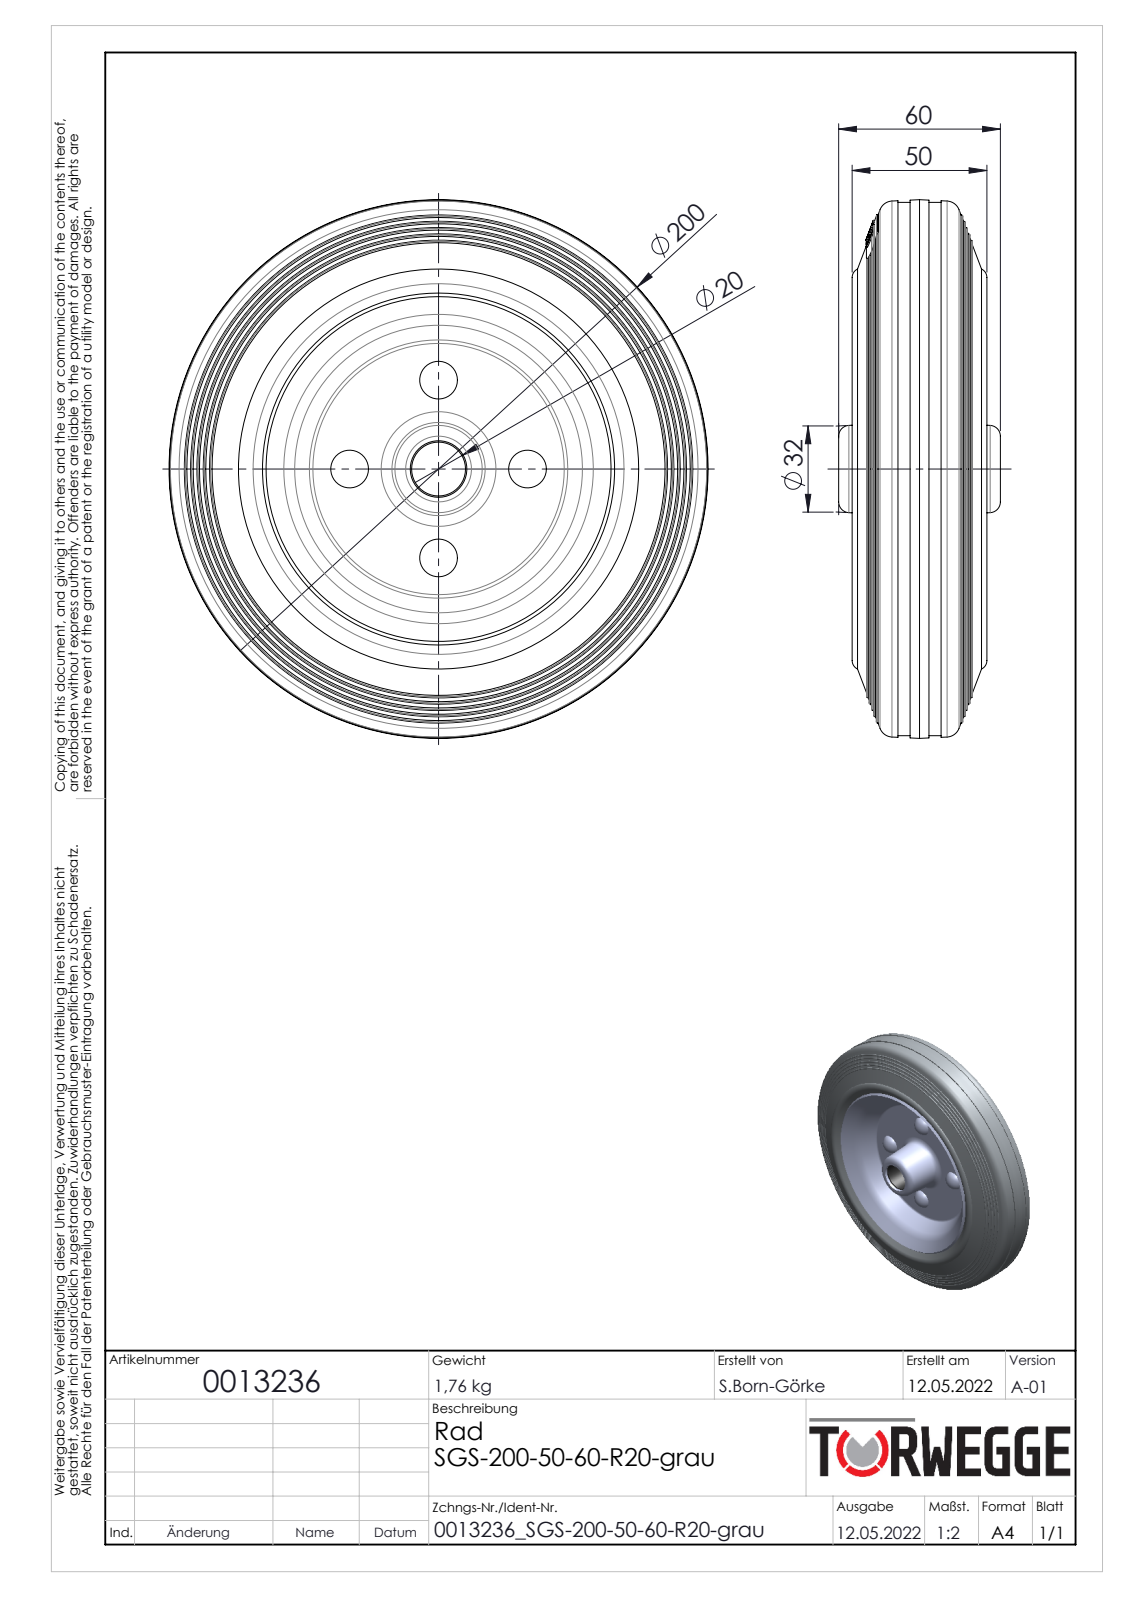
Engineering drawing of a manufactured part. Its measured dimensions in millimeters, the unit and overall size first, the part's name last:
Units: millimetres
Overall size (bounding box): 200 × 200 × 60
Round holes (diameter × count): ⌀8 ×4, ⌀20 ×1, ⌀21 ×1
Round bosses / shafts (diameter × count): ⌀198 ×1, ⌀30 ×1
Main face-to-face distances: 2, 4, 1.5, 3.5, 5.5, 24, 25.5, 27.5, 29.5, 31
Hole centre spacings: 33, 46.67, 66
Volume: 933 812 mm³ · Surface area: 169 003 mm²
Bodies: 18 solids, 347 faces (60 planar, 36 cylindrical, 251 other)
Part name (STEP PRODUCT): 0013236
STEP written by: SolidWorks 2020 (AUTOMOTIVE_DESIGN)
